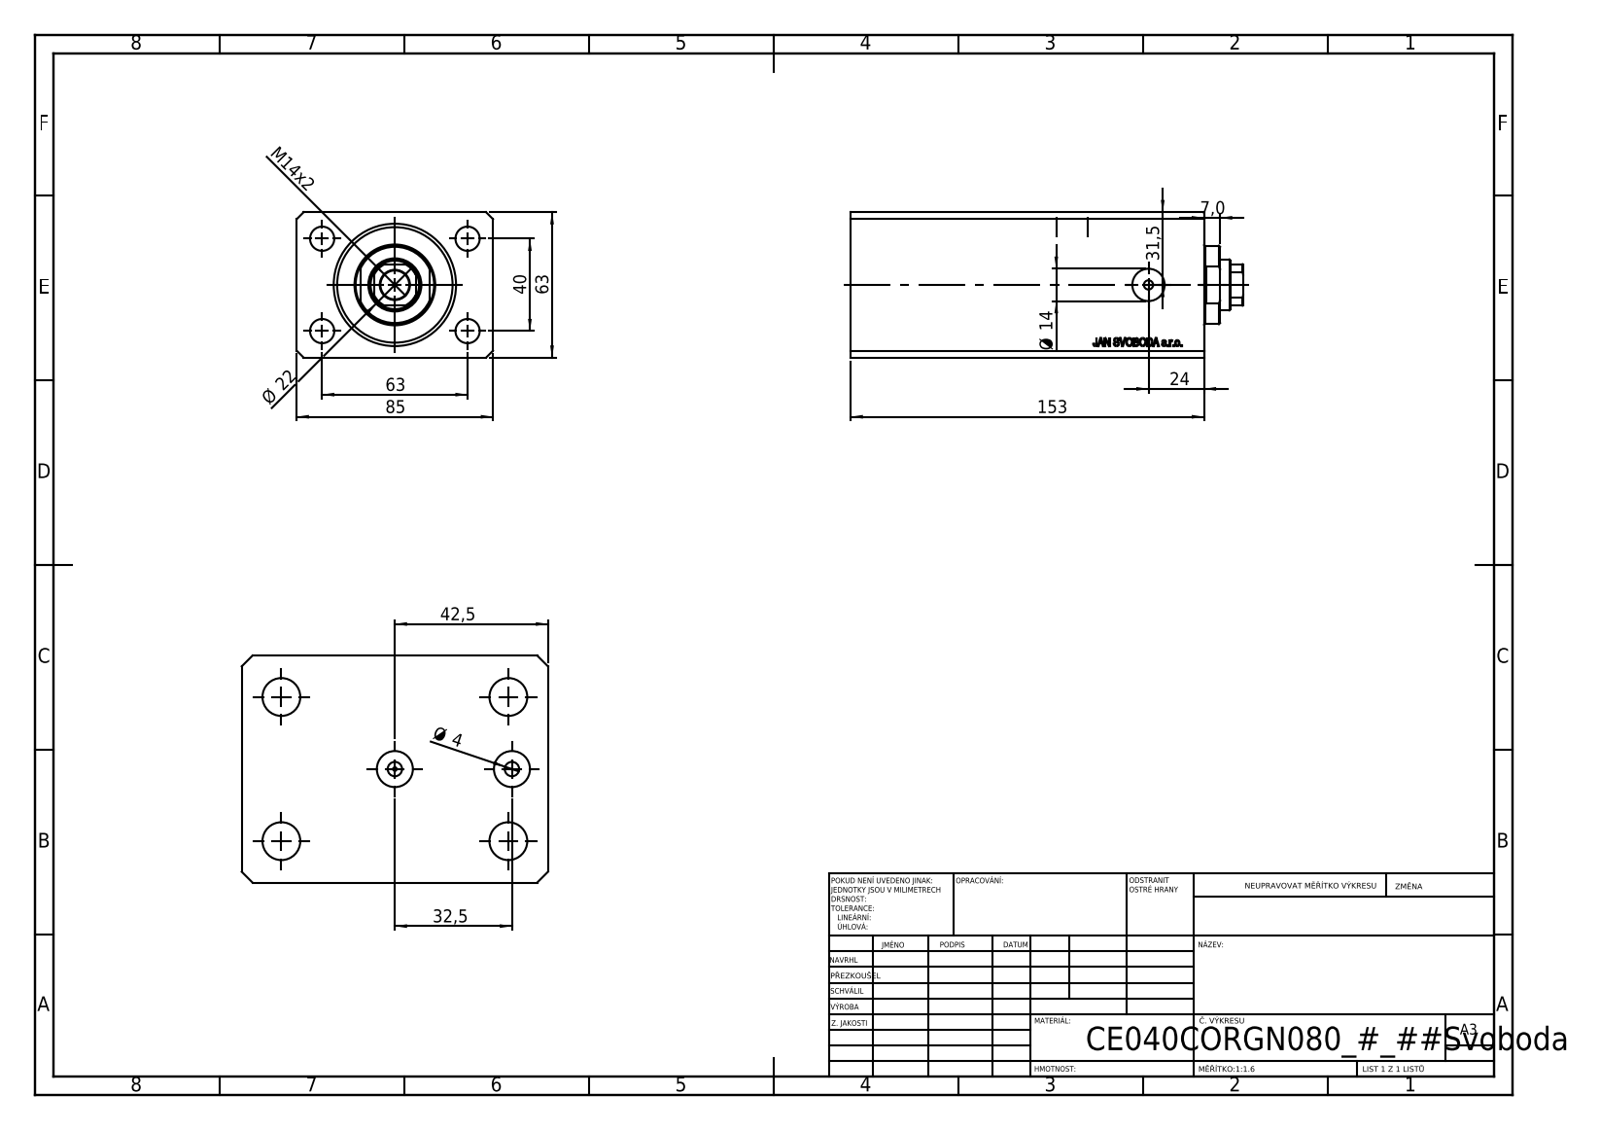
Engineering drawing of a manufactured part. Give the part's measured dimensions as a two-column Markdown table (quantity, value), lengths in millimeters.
| quantity | value |
| --- | --- |
| part name | V250CE_VC_C; V250CE_C_Body; V250CE_C_VCP |
| STEP written by | SolidWorks 2019 (CONFIG_CONTROL_DESIGN) |
| units | millimeters |
| bodies | 3 solids, 868 faces (428 planar, 46 cylindrical, 394 other) |
| overall size | 170 × 85 × 63 |
| volume | 696 416 mm³ |
| surface area | 121 092 mm² |
| round holes (diameter × count) | 4 × 4, 10.5 × 4, 10 × 2, 14 × 2, 1.25 × 1, 12.5 × 1, 22 × 1, 40 × 1, 53 × 1 |
| round bosses / shafts (diameter × count) | 34 × 1 |
| partial cylindrical surfaces (radius × count) | 10.5 × 1 |
| main face-to-face distances | 63, 85, 153, 17, 136, 11.4, 124.6, 141.6, 100.4, 80 |
| hole center spacings | 37.31, 20.02, 40, 63, 67.05, 74.63, 32.5, 105 |
